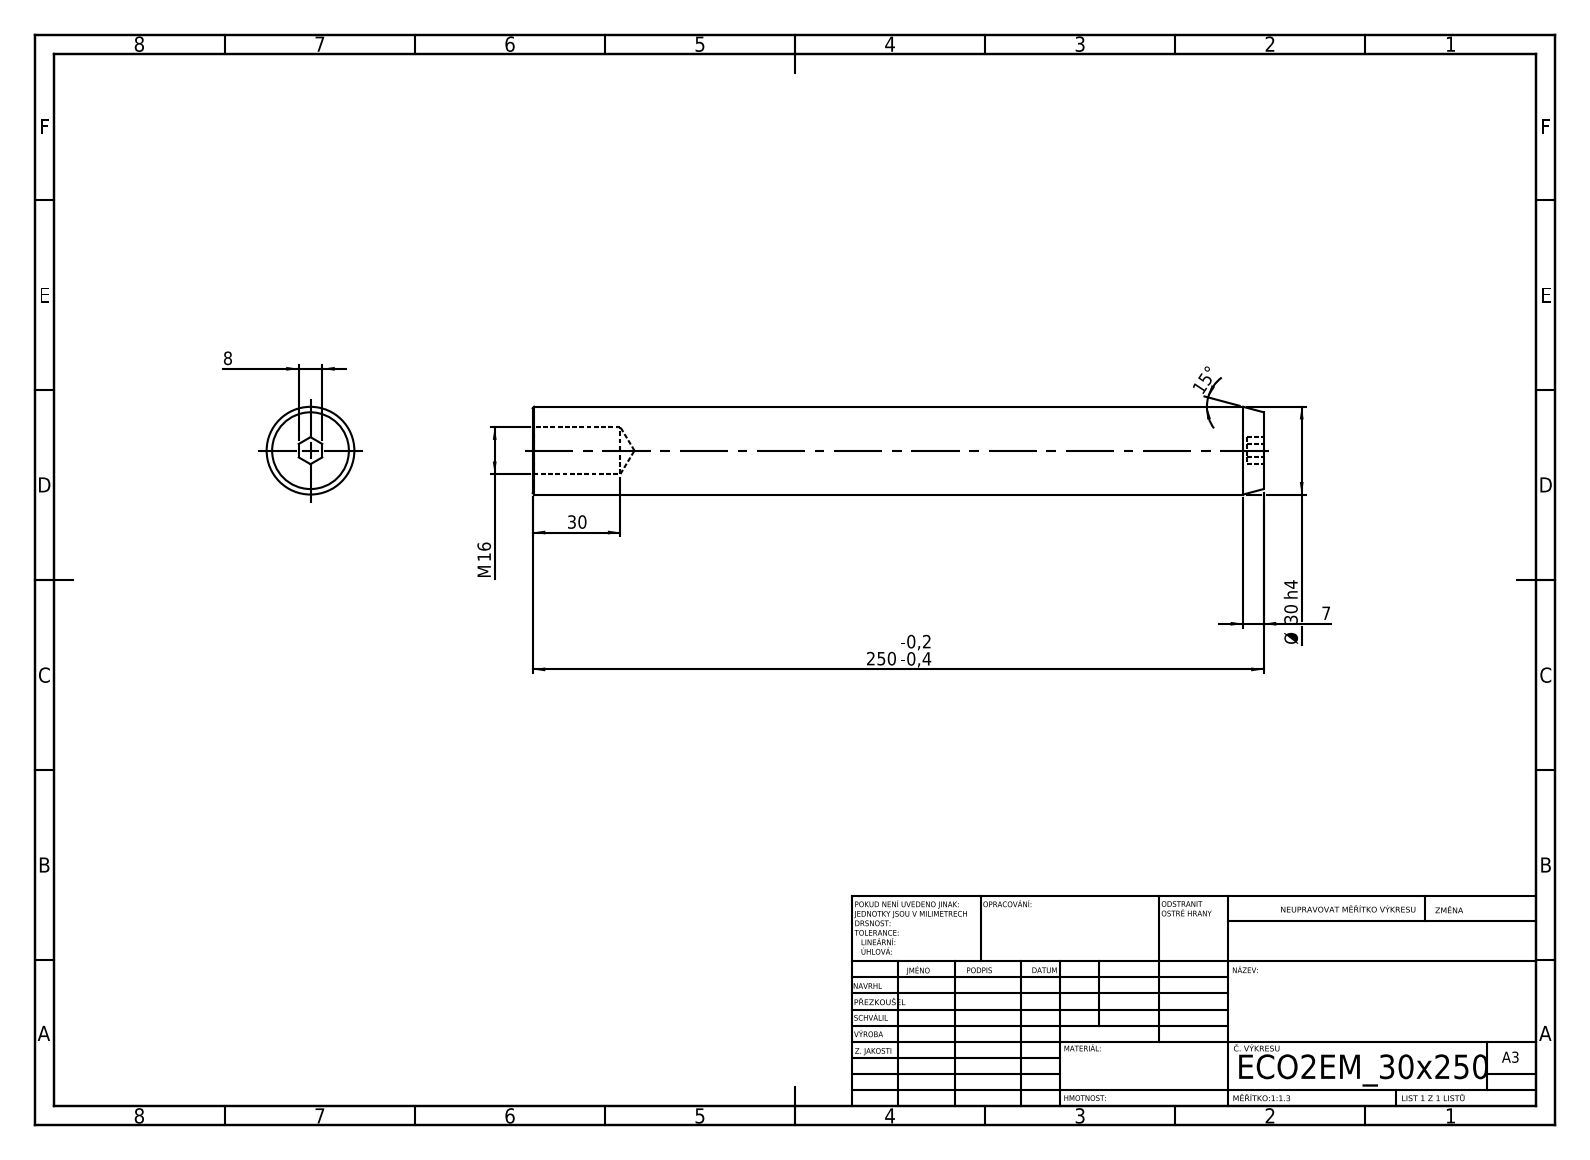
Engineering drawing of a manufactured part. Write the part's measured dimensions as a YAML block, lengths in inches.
step_written_by: "SolidWorks 2019 (CONFIG_CONTROL_DESIGN)"
units: inches
bodies: {solids: 1, faces: 21, planar: 9, cylindrical: 4, other: 8}
overall_size: [9.843, 1.181, 1.181]
volume: 10.34
surface_area: 41.01
round_holes:
  - {diameter: 0.63, count: 1}
round_bosses_or_shafts:
  - {diameter: 1.181, count: 1}
face_to_face_distances: [9.843, 0.315, 0.228, 9.614]
